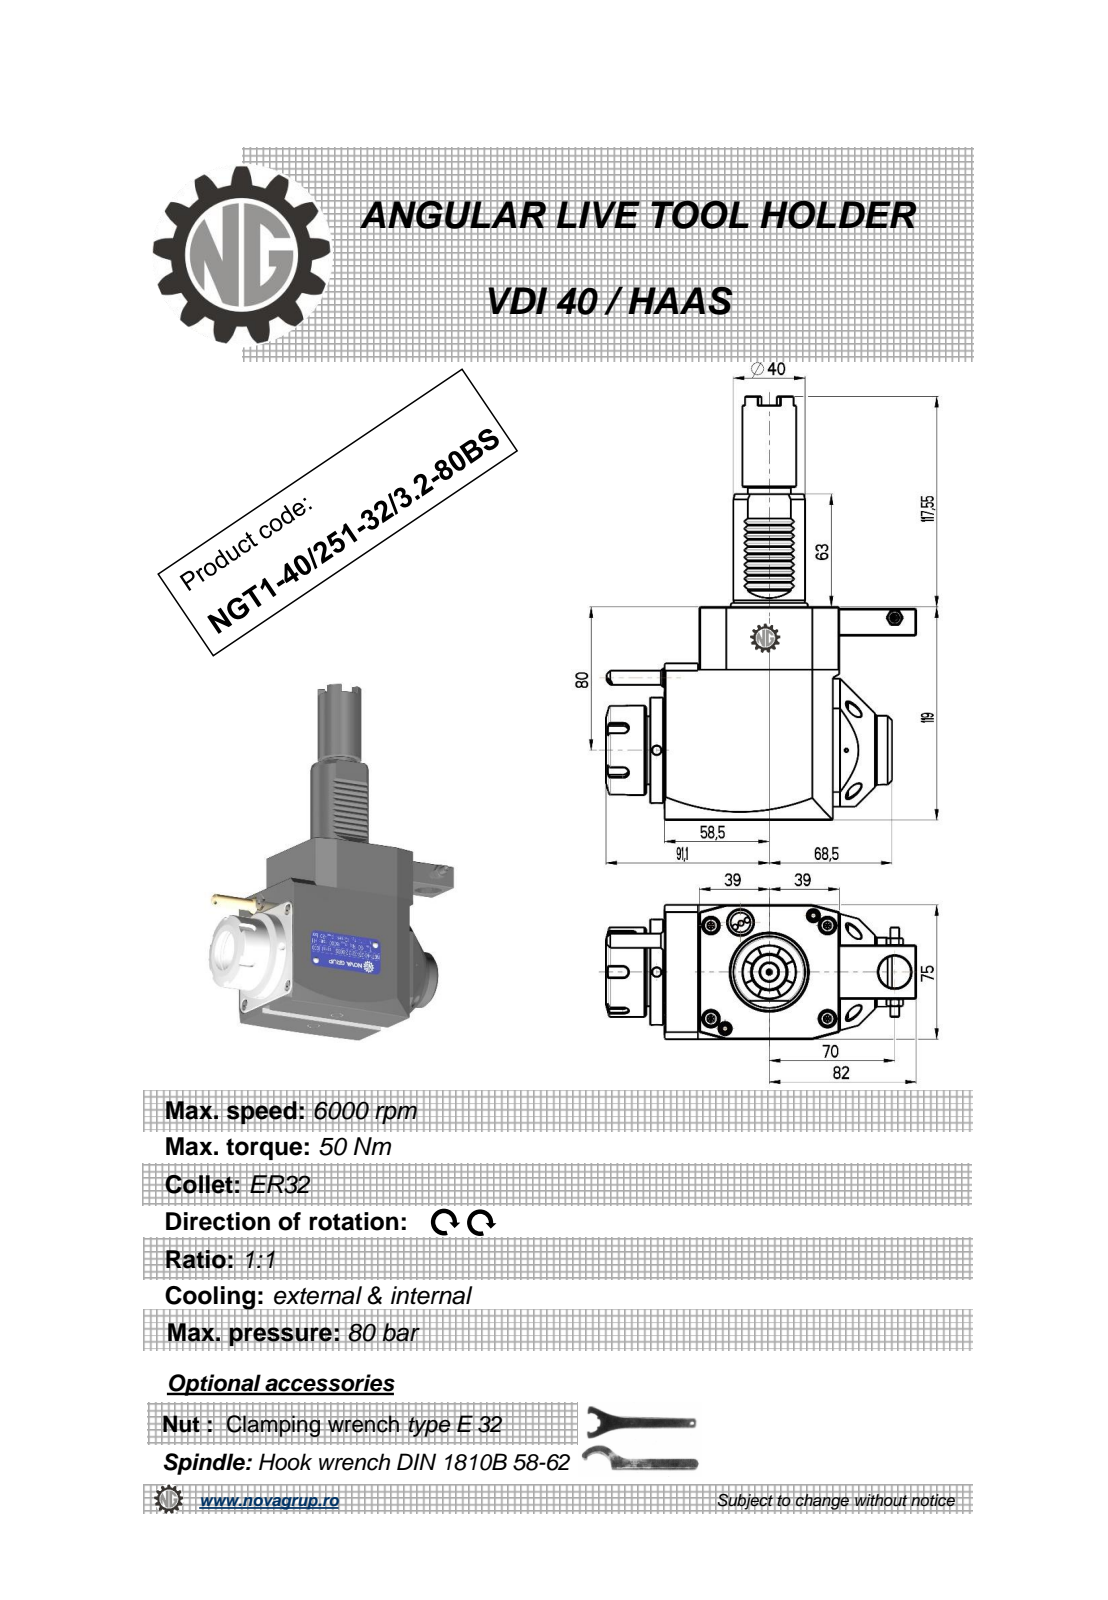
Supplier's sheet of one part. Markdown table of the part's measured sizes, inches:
| quantity | value |
| --- | --- |
| part name | NGT1_40_251_32_3_2_80BS |
| STEP written by | PRO/ENGINEER BY PARAMETRIC TECHNOLOGY CORPORATION, 2010280 (CONFIG_CONTROL_DESIGN) |
| units | inches |
| bodies | 1 solid, 484 faces (239 planar, 99 cylindrical, 146 other) |
| overall size | 9.313 × 6.815 × 2.953 |
| volume | 64.75 in³ |
| surface area | 135.1 in² |
| round holes (diameter × count) | 0.197 × 3, 0.118 × 1, 0.165 × 1, 0.374 × 1, 0.709 × 1, 1.063 × 1, 1.811 × 1 |
| round bosses / shafts (diameter × count) | 2.323 × 1, 1.969 × 1, 1.811 × 1, 1.614 × 1, 1.575 × 1, 1.516 × 1, 1.181 × 1, 0.945 × 1 |
| partial cylindrical surfaces (radius × count) | 0.01 × 12, 0.012 × 10, 0.008 × 6, 0.118 × 5, 0.228 × 2, 0.236 × 2, 23.622 × 2, 0.02 × 1 |
| main face-to-face distances | 2.953, 4.685, 0.768, 3.839, 3.071, 0.76, 3.831, 1.083, 0.039, 0.138 |
| hole center spacings | 1.436, 1.737, 2.854, 5.226, 5.983 |
